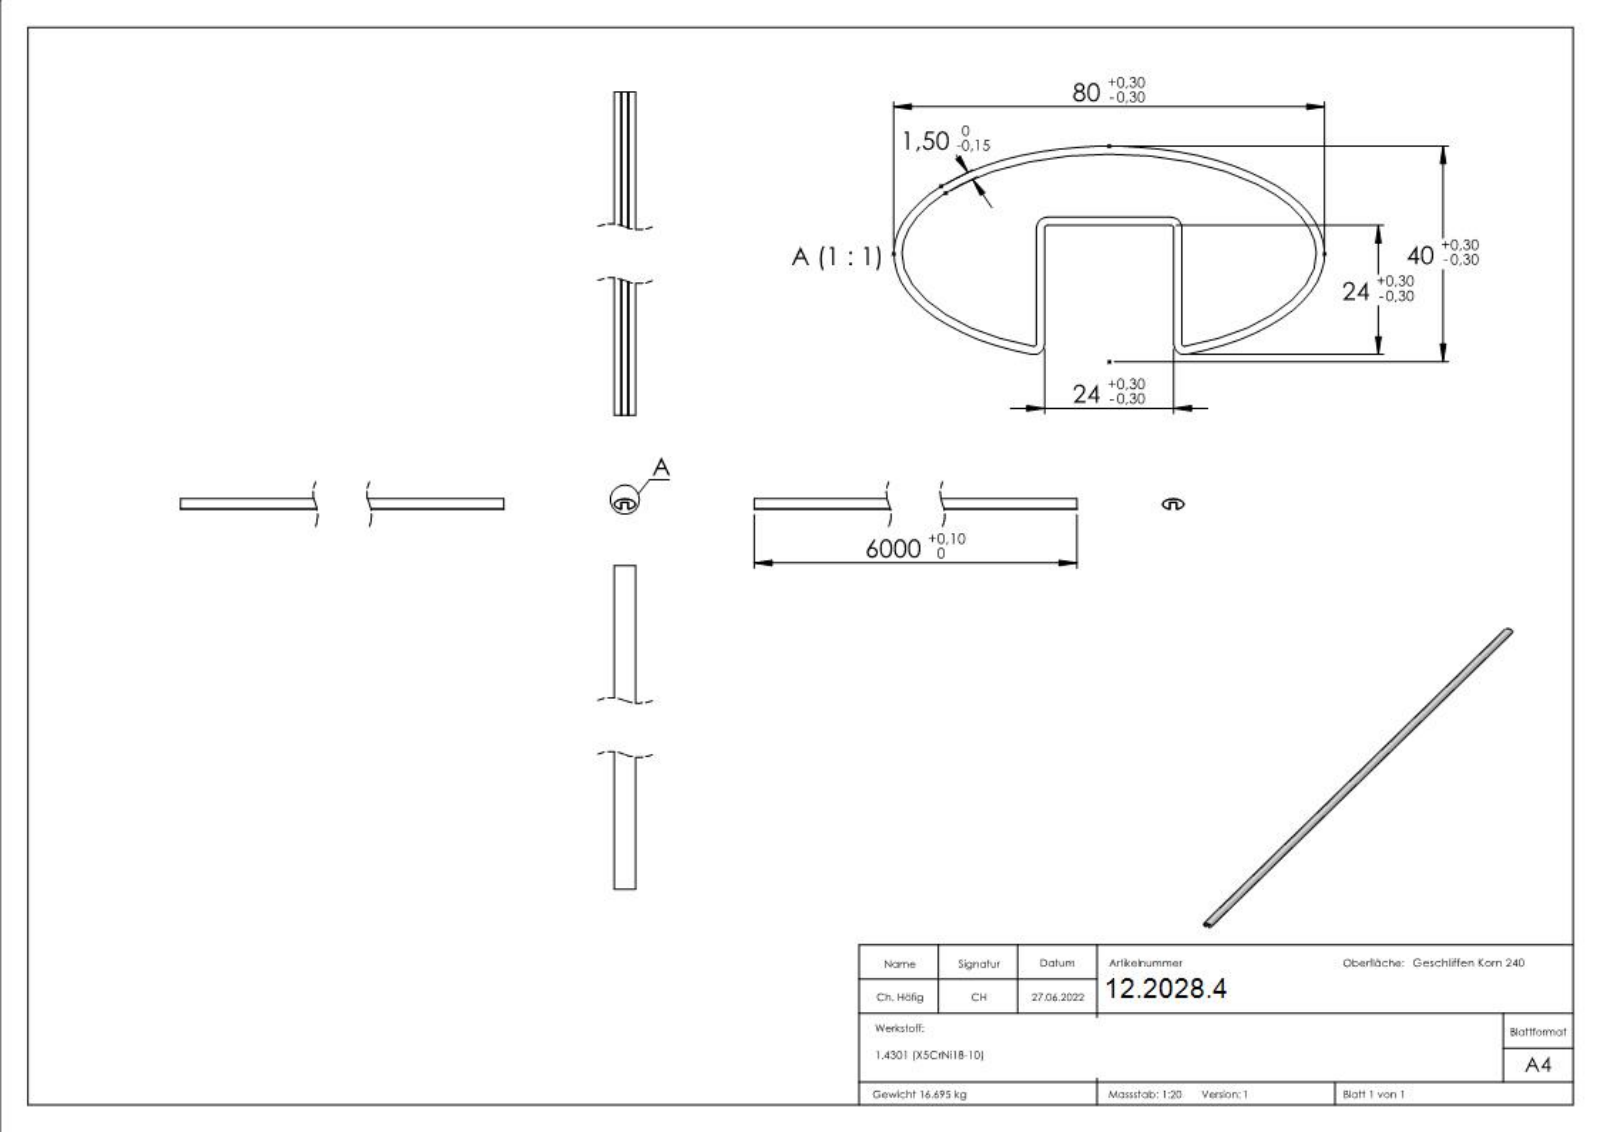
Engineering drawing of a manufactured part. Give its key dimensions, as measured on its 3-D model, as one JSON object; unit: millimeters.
{"part_name": "60332-240", "step_written_by": "SolidWorks 2018 (CONFIG_CONTROL_DESIGN)", "units": "millimeters", "bodies": {"solids": 1, "faces": 292, "planar": 147, "cylindrical": 8, "other": 137}, "overall_size": [6000, 80, 38.7], "volume_mm3": 2192000, "surface_area_mm2": 2820000, "partial_cylinders_radius": [[0.5, 4], [2, 4]], "face_to_face_distances": [1.5, 25.5, 27, 24, 6000, 1.4, 3.27, 1.82, 0.34, 13.5]}
